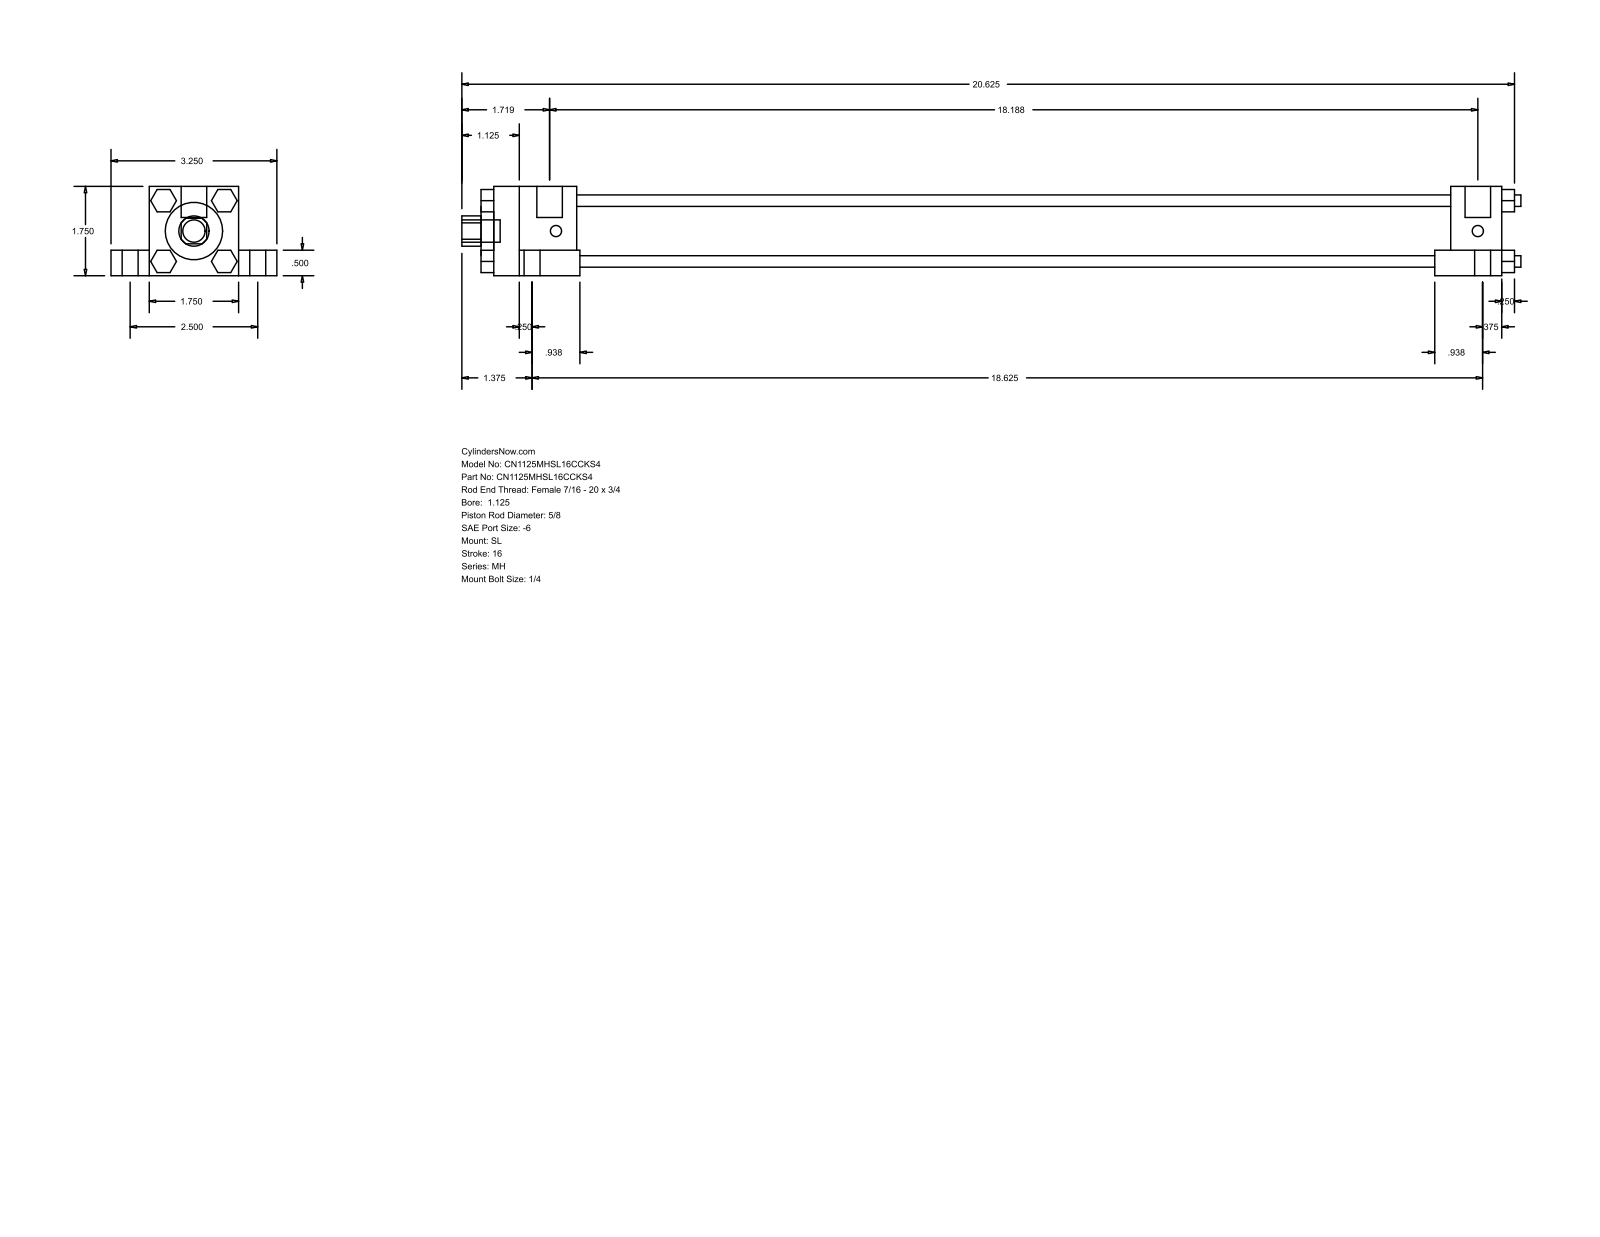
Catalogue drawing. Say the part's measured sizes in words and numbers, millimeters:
The part is named "MH_SL__0112_0.625". Its 3-D file was written by "GSSL Pune (CONFIG_CONTROL_DESIGN)". It is 0 solids with 150 faces: 114 planar, 36 cylindrical and 0 other. Overall it measures 527.05 by 82.55 by 44.45 millimeters. Round holes: 1 of diameter 15.88, 1 of diameter 28.57, 1 of diameter 34.92. Round bosses or shafts: 4 of diameter 14.29, 4 of diameter 7.94, 4 of diameter 5.71, 4 of diameter 5.56, 2 of diameter 12.7, 1 of diameter 11.11. Partial cylindrical surfaces (rounded edges, fillets, slot ends): 1 of radius 7.54. The main face-to-face distances are 44.46, 31.76, 19.04, 12.7, 63.5, 11.11, 434.97, 460.37, 25.4, 41.27.
